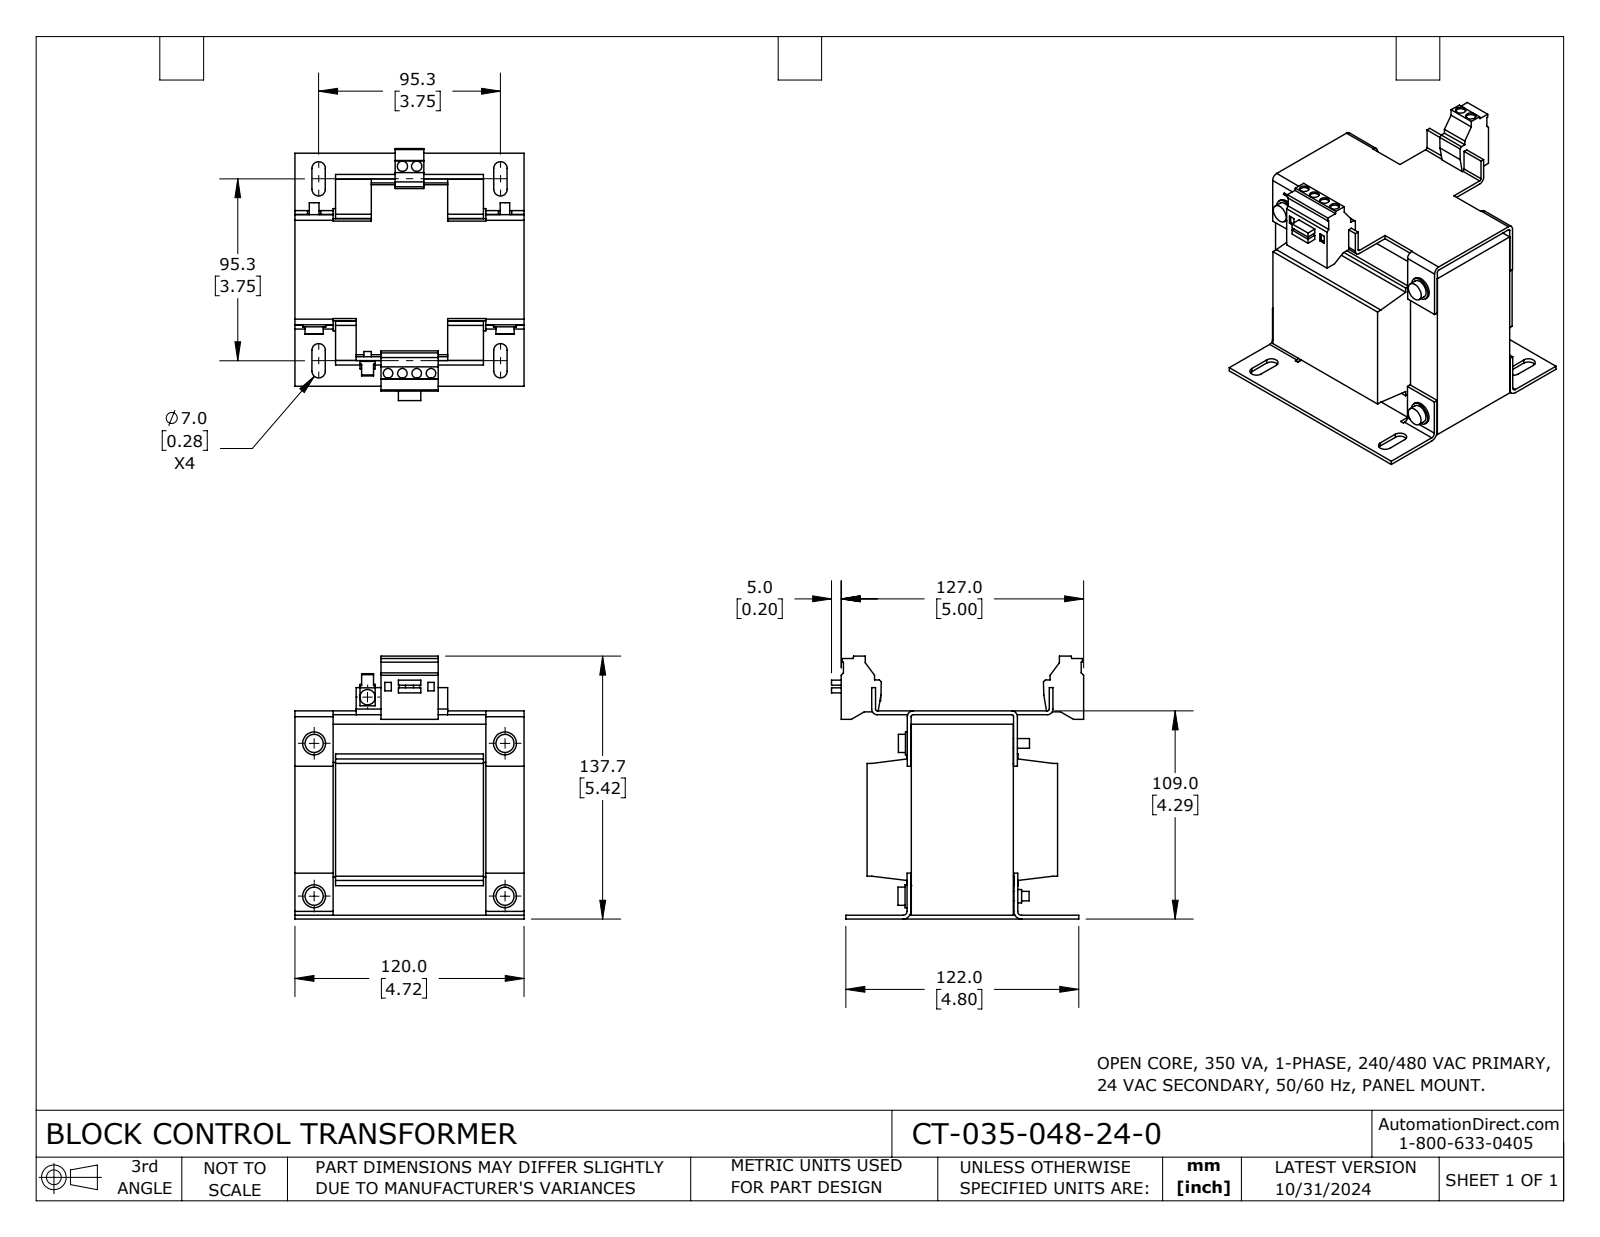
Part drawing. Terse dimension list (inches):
name: CT-035-048-24-0
written by: SolidWorks 2023 (CONFIG_CONTROL_DESIGN)
unit: in
bodies: 1 solid, 327 faces (235 planar, 92 cylindrical, 0 other)
size: 5.421 × 5.197 × 4.724
volume: 56.7 in³; area: 209.4 in²
holes: 4× ⌀0.197, 2× ⌀0.213
bosses: 4× ⌀0.472, 4× ⌀0.374, 4× ⌀0.236, 4× ⌀0.197, 2× ⌀0.276, 1× ⌀0.315, 1× ⌀0.157
rounds: 8× R0.138, 4× R0.039, 4× R0.118, 2× R0.079, 2× R0.157
face distances: 0.079, 4.213, 3.937, 0.837, 3.888, 0.787, 0.911, 3.018, 3.1, 3.15
hole spacings: 0.295, 4.278, 0.591, 4.268, 4.308, 0.886
